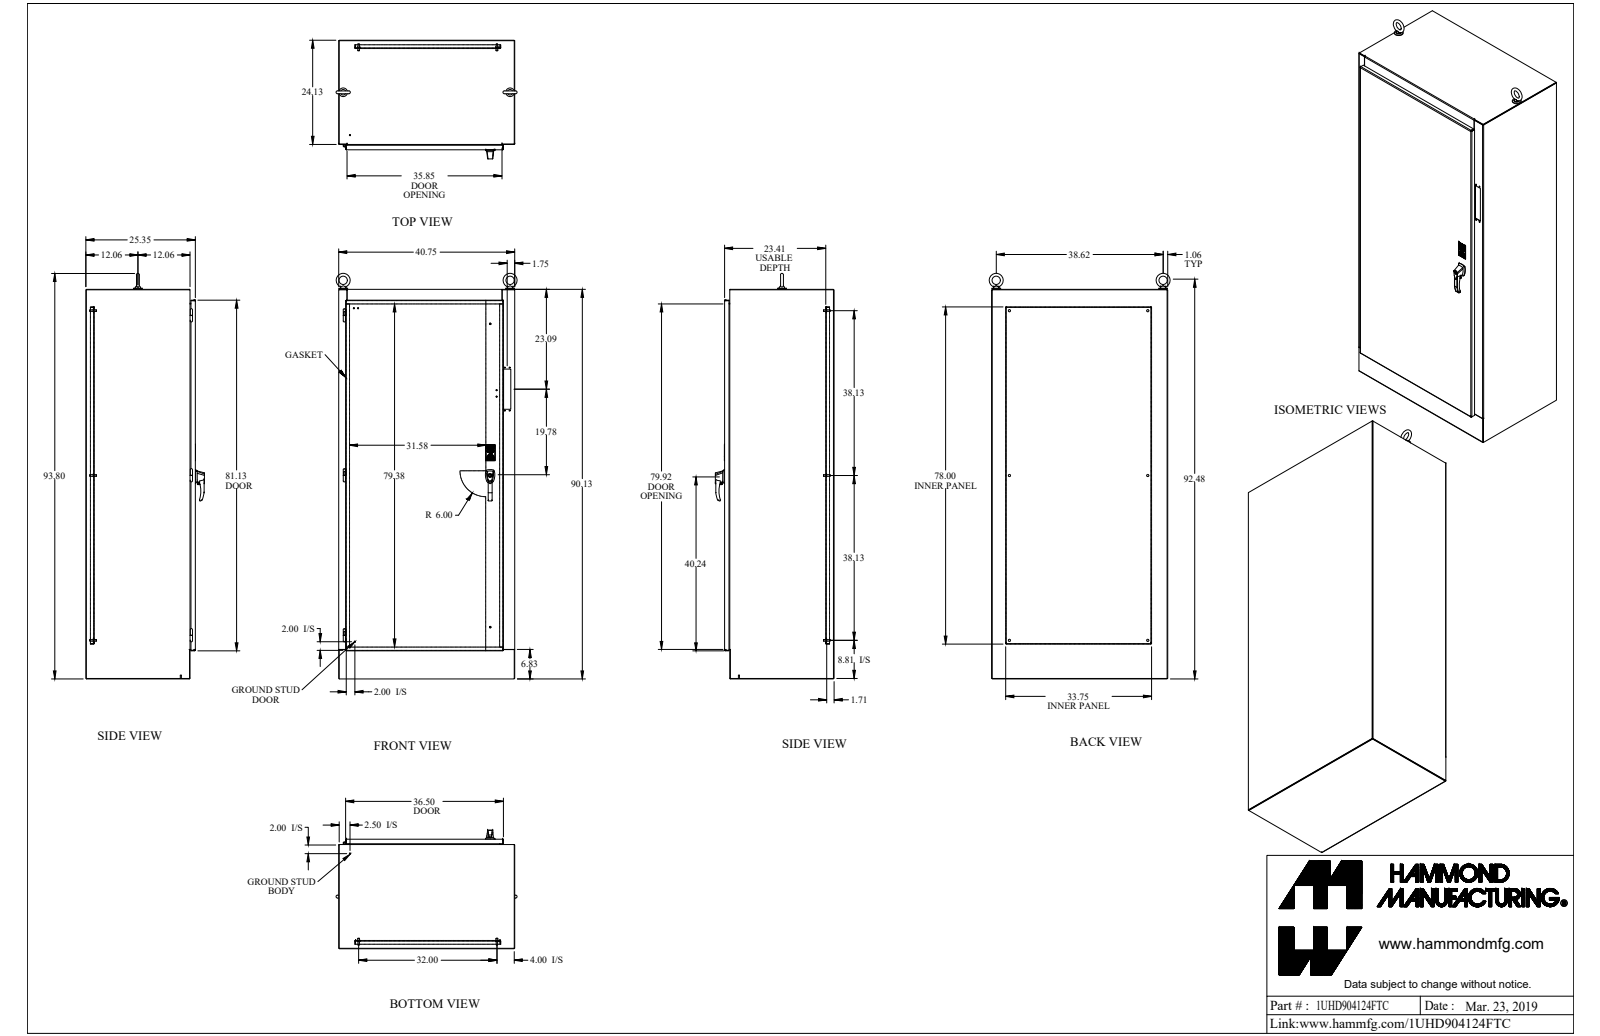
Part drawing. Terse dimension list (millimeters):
name: 1UHD904124FTC
written by: SolidWorks 2018 (AUTOMOTIVE_DESIGN)
unit: mm
bodies: 102 solids, 1773 faces (978 planar, 482 cylindrical, 313 other)
size: 2382.5 × 1063.5 × 697.6
volume: 38 230 000 mm³; area: 24 120 000 mm²
holes: 7× ⌀7.8, 7× ⌀8.9, 6× ⌀7.1, 6× ⌀11.3, 6× ⌀14.3, 5× ⌀5, 3× ⌀6.4, 3× ⌀8, 2× ⌀4.2, 2× ⌀6.5, 2× ⌀6.5, 2× ⌀7.1
bosses: 10× ⌀6.4, 8× ⌀25.4, 7× ⌀9.5, 6× ⌀16.5, 6× ⌀8.4, 4× ⌀7.1, 4× ⌀4.8, 3× ⌀15.9
rounds: 39× R1.5, 28× R4.7, 25× R12.7, 22× R3.2, 16× R0.4, 12× R0.8, 8× R3.3, 7× R19.1
face distances: 3.2, 640.7, 3.2, 637.5, 643.9, 49.2, 46, 591.5, 594.7, 46
hole spacings: 812.8, 25.4, 28.6, 28.6, 32.7, 50.8, 188.8, 189.6
